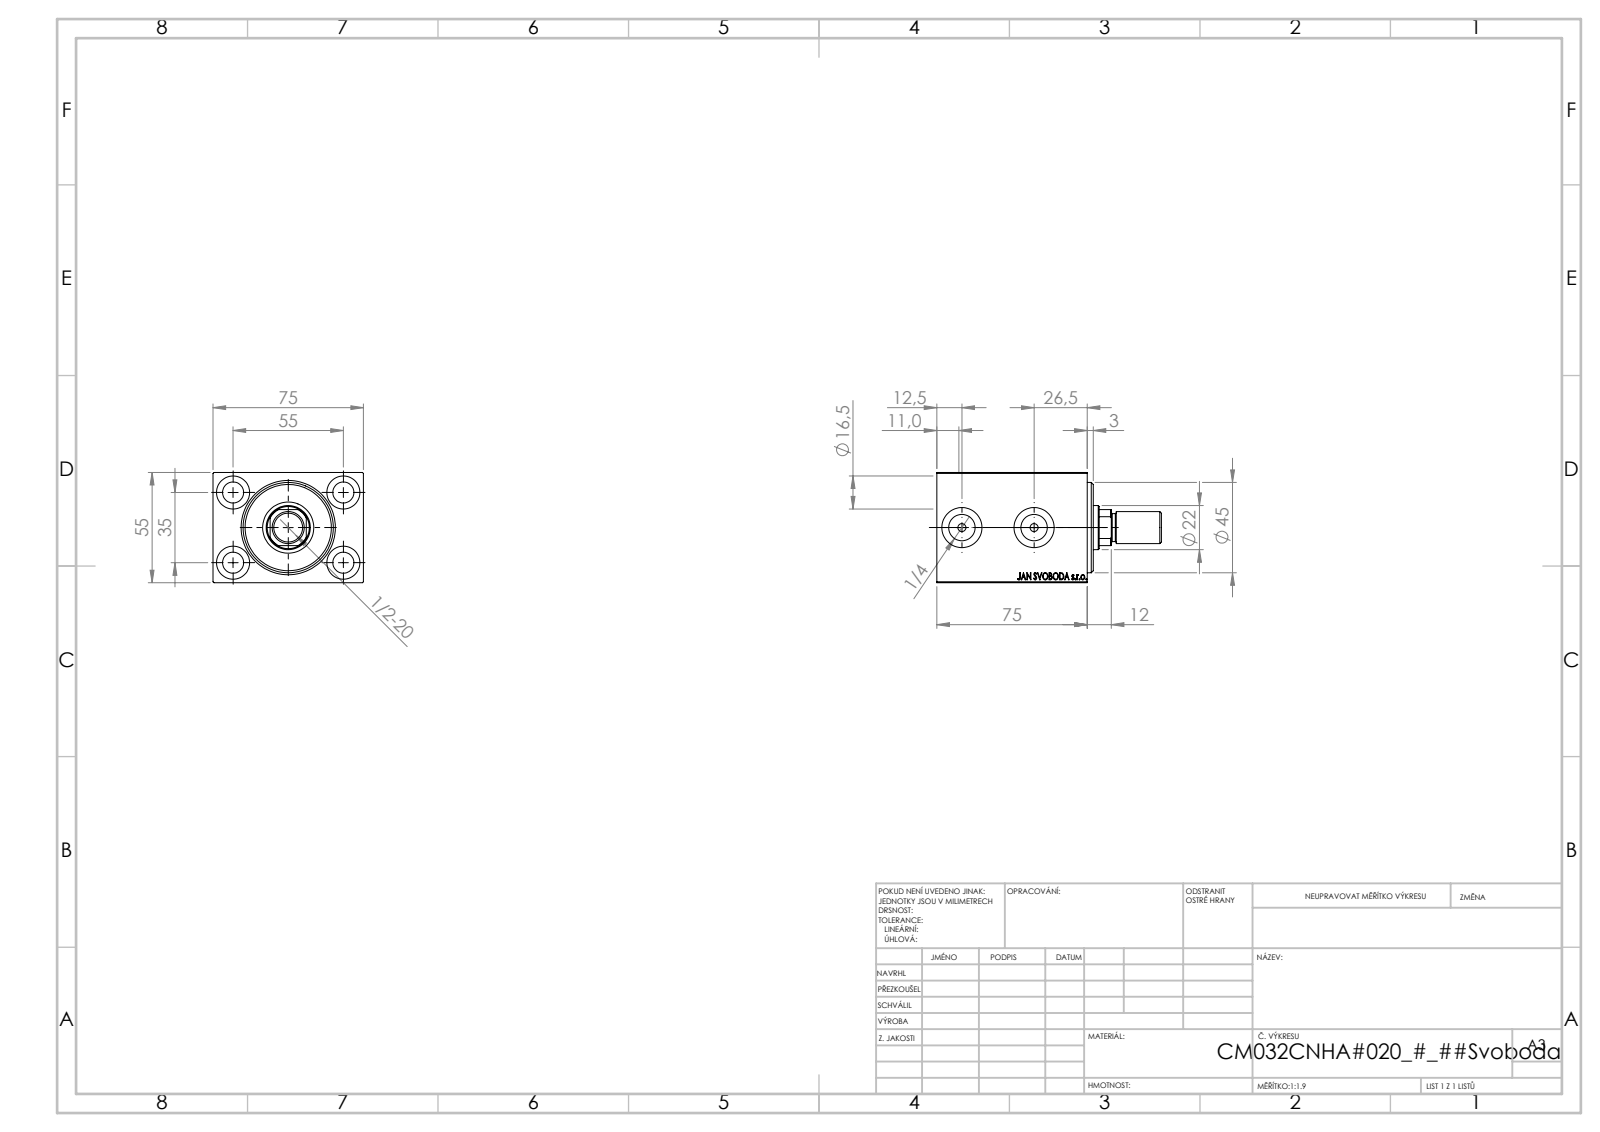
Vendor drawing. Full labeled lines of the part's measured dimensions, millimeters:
Part name (STEP PRODUCT): V450CM_VC_B; V450CM_C_VCP; V450CM_MALE_METRIC; V450CM_C_Body
STEP written by: SolidWorks 2019 (CONFIG_CONTROL_DESIGN)
Units: millimetres
Bodies: 4 solids, 875 faces (411 planar, 64 cylindrical, 400 other)
Overall size (bounding box): 112 × 75 × 55
Volume: 270 589 mm³ · Surface area: 62 010 mm²
Round holes (diameter × count): ⌀10.5 ×5, ⌀16.5 ×4, ⌀4 ×2, ⌀13.16 ×2, ⌀20 ×2, ⌀22 ×1, ⌀25.5 ×1, ⌀32 ×1, ⌀34 ×1, ⌀45 ×1
Round bosses / shafts (diameter × count): ⌀16 ×1, ⌀14 ×1
Partial cylindrical surfaces — rounded edges, fillets, slot ends (radius × count): R10.5 ×1
Main face-to-face distances: 55, 75, 10, 65, 70, 5, 60, 53, 11, 64
Hole centre spacings: 32.6, 35, 55, 65.19, 36
